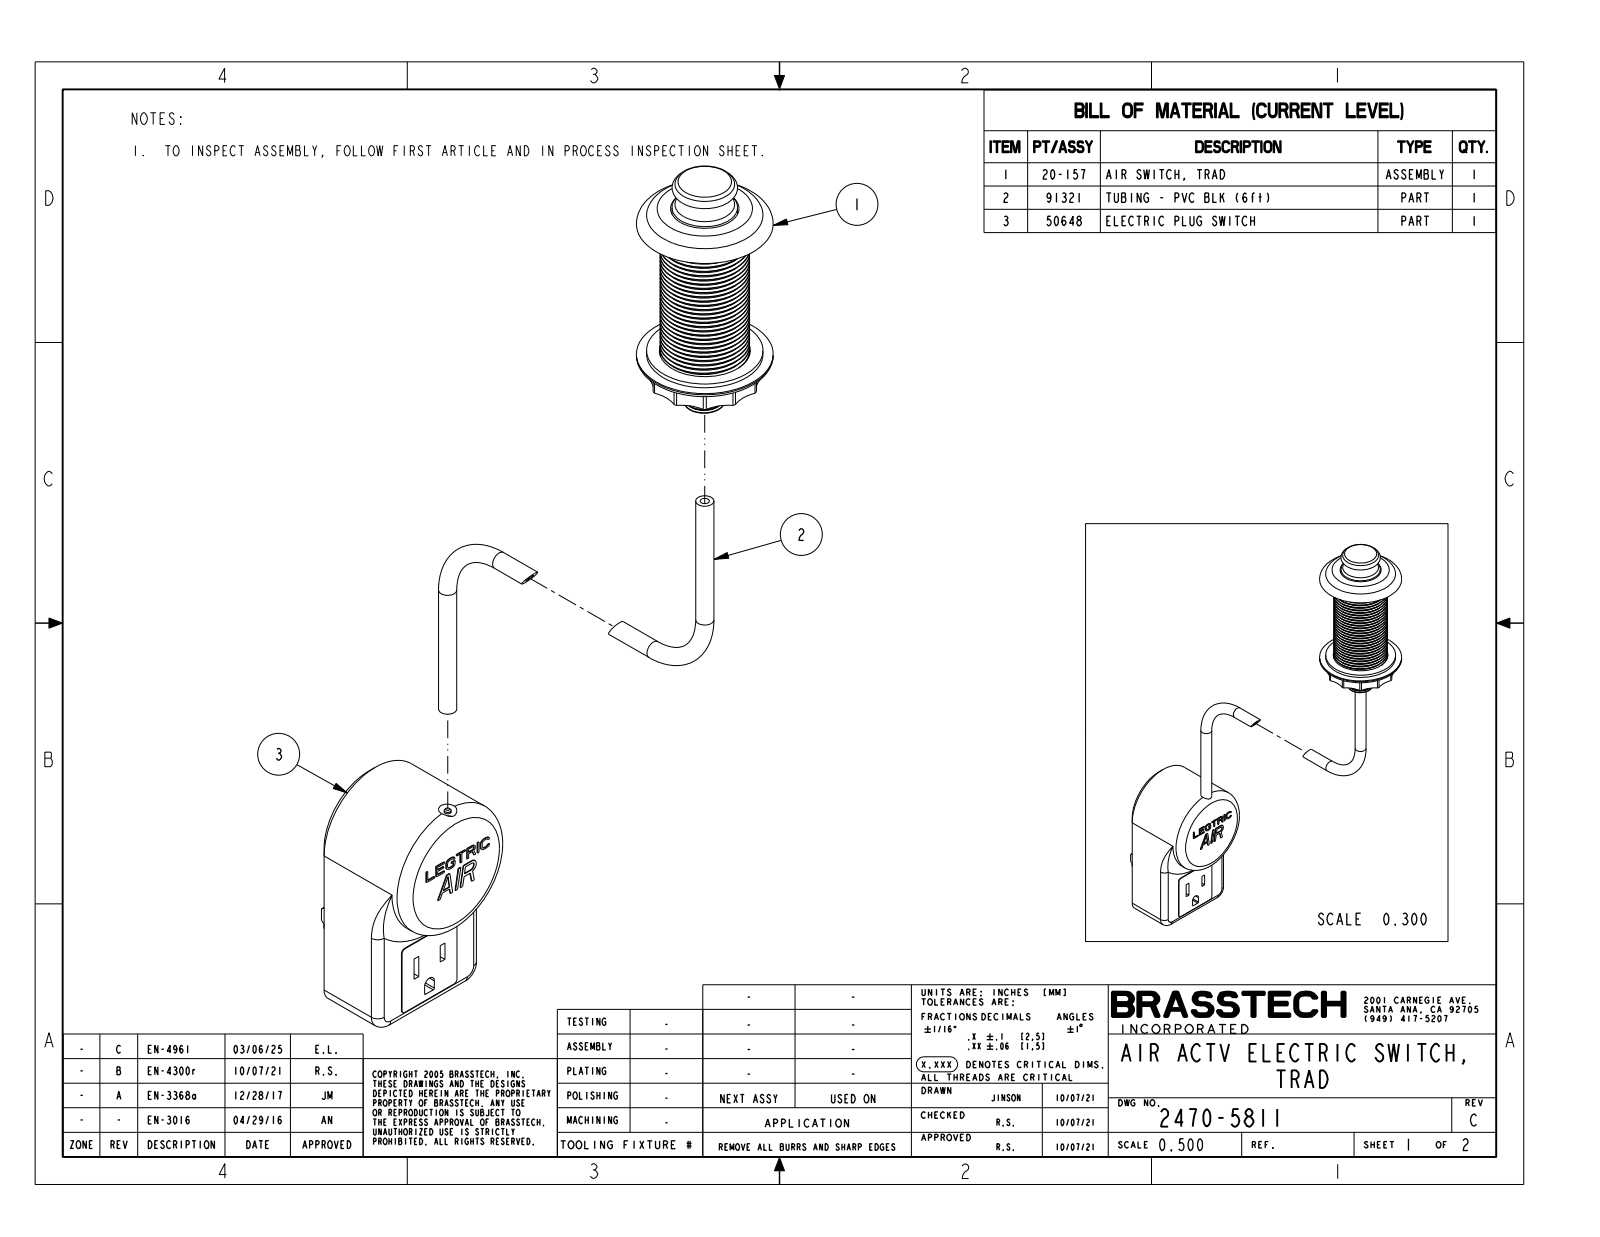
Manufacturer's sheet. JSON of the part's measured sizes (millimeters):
{"part_name": "2470-5811", "step_written_by": "CREO PARAMETRIC BY PTC INC, 2018400 (AUTOMOTIVE_DESIGN)", "units": "millimeters", "bodies": {"solids": 3, "faces": 471, "planar": 253, "cylindrical": 146, "other": 72}, "overall_size": [325.2, 211.2, 50.5], "volume_mm3": 224300, "surface_area_mm2": 43120, "round_holes": [[3.2, 4], [23.9, 1], [31.8, 1]], "round_bosses_or_shafts": [[6.4, 3], [50.5, 1], [47.8, 1], [40.6, 1], [31.2, 1], [28.8, 1], [22.9, 1], [14.1, 1]], "partial_cylinders_radius": [[12.7, 12], [1.5, 4], [3.2, 3], [0.5, 2], [6.4, 2], [2.4, 1], [20.6, 1]], "face_to_face_distances": [50.5, 43.2, 2, 9.1, 305.9, 13.2, 30, 29.7, 13.5, 250.3], "hole_center_spacings": [127]}
